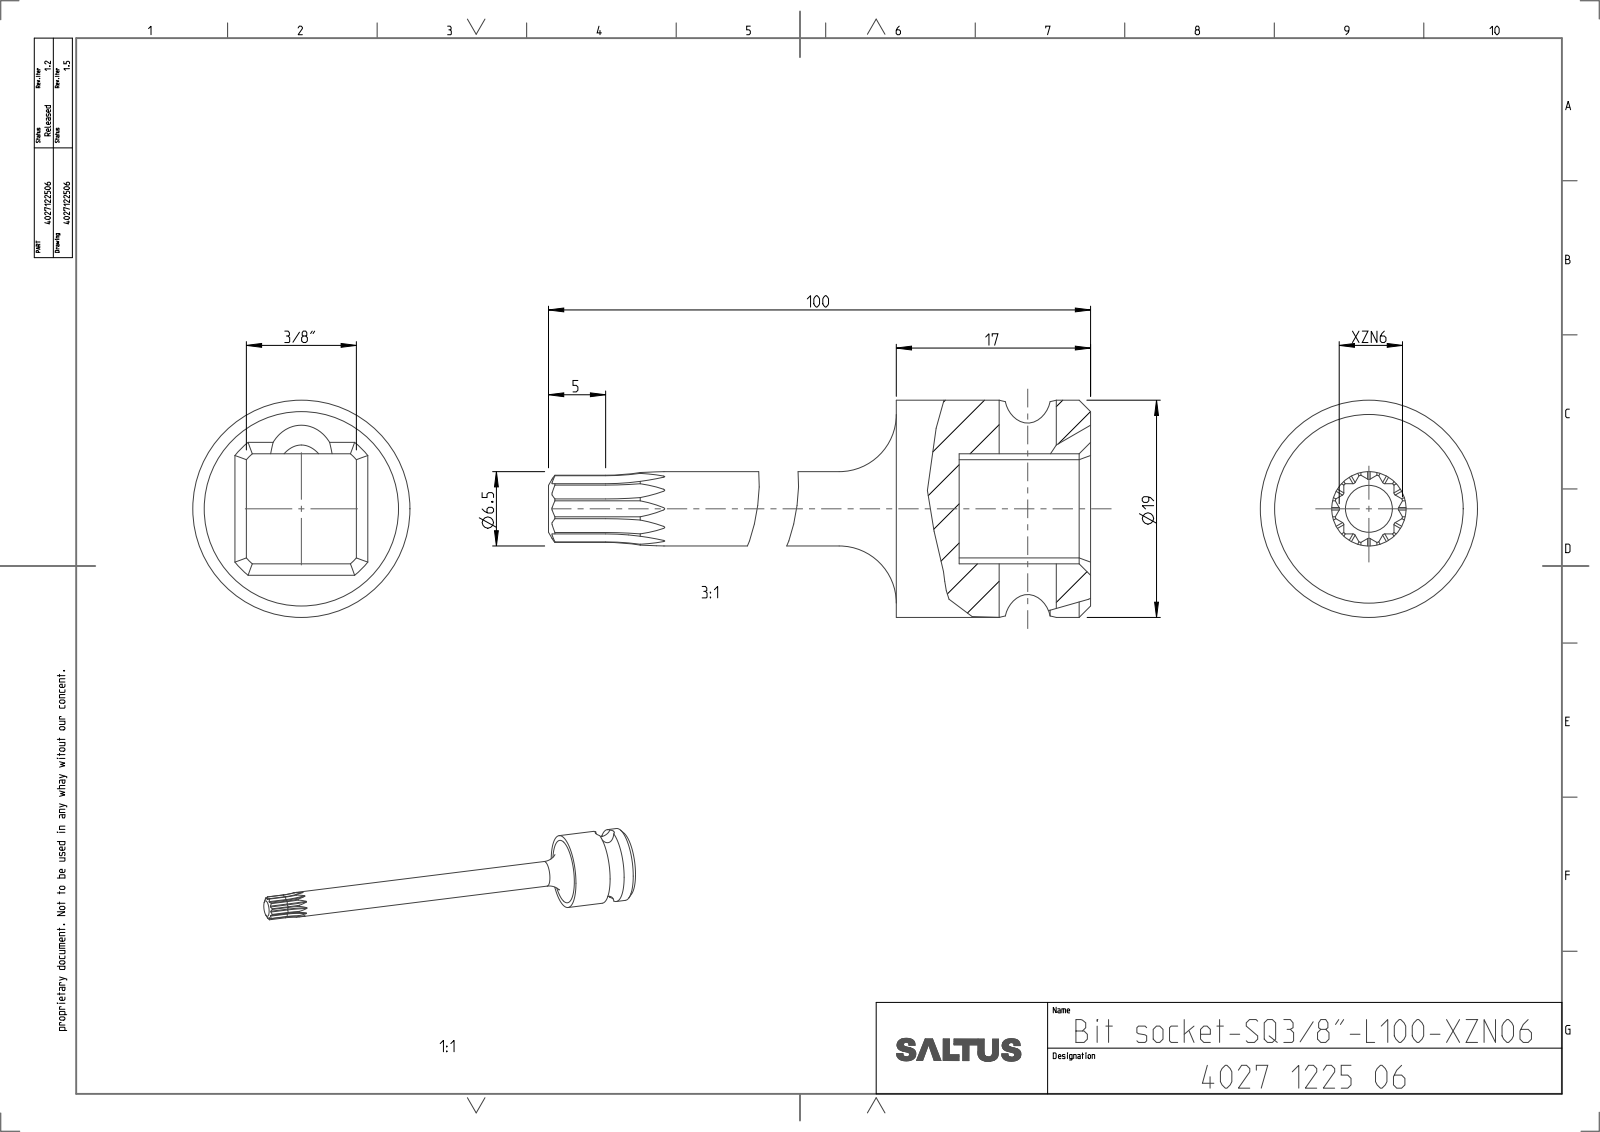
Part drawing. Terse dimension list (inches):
name: 4027122506
written by: CREO PARAMETRIC BY PTC INC, 2022414 (CONFIG_CONTROL_DESIGN)
unit: in
bodies: 1 solid, 136 faces (37 planar, 39 cylindrical, 60 other)
size: 3.937 × 0.748 × 0.748
volume: 0.374 in³; area: 5.727 in²
holes: 1× ⌀0.197
bosses: 1× ⌀0.748, 1× ⌀0.256
rounds: 12× R0.009, 1× R0.118, 1× R0.119, 1× R0.254
face distances: 0.379, 0.453, 0.669, 0.217, 0.173, 0.103, 0.276, 3.937, 3.484, 3.268
